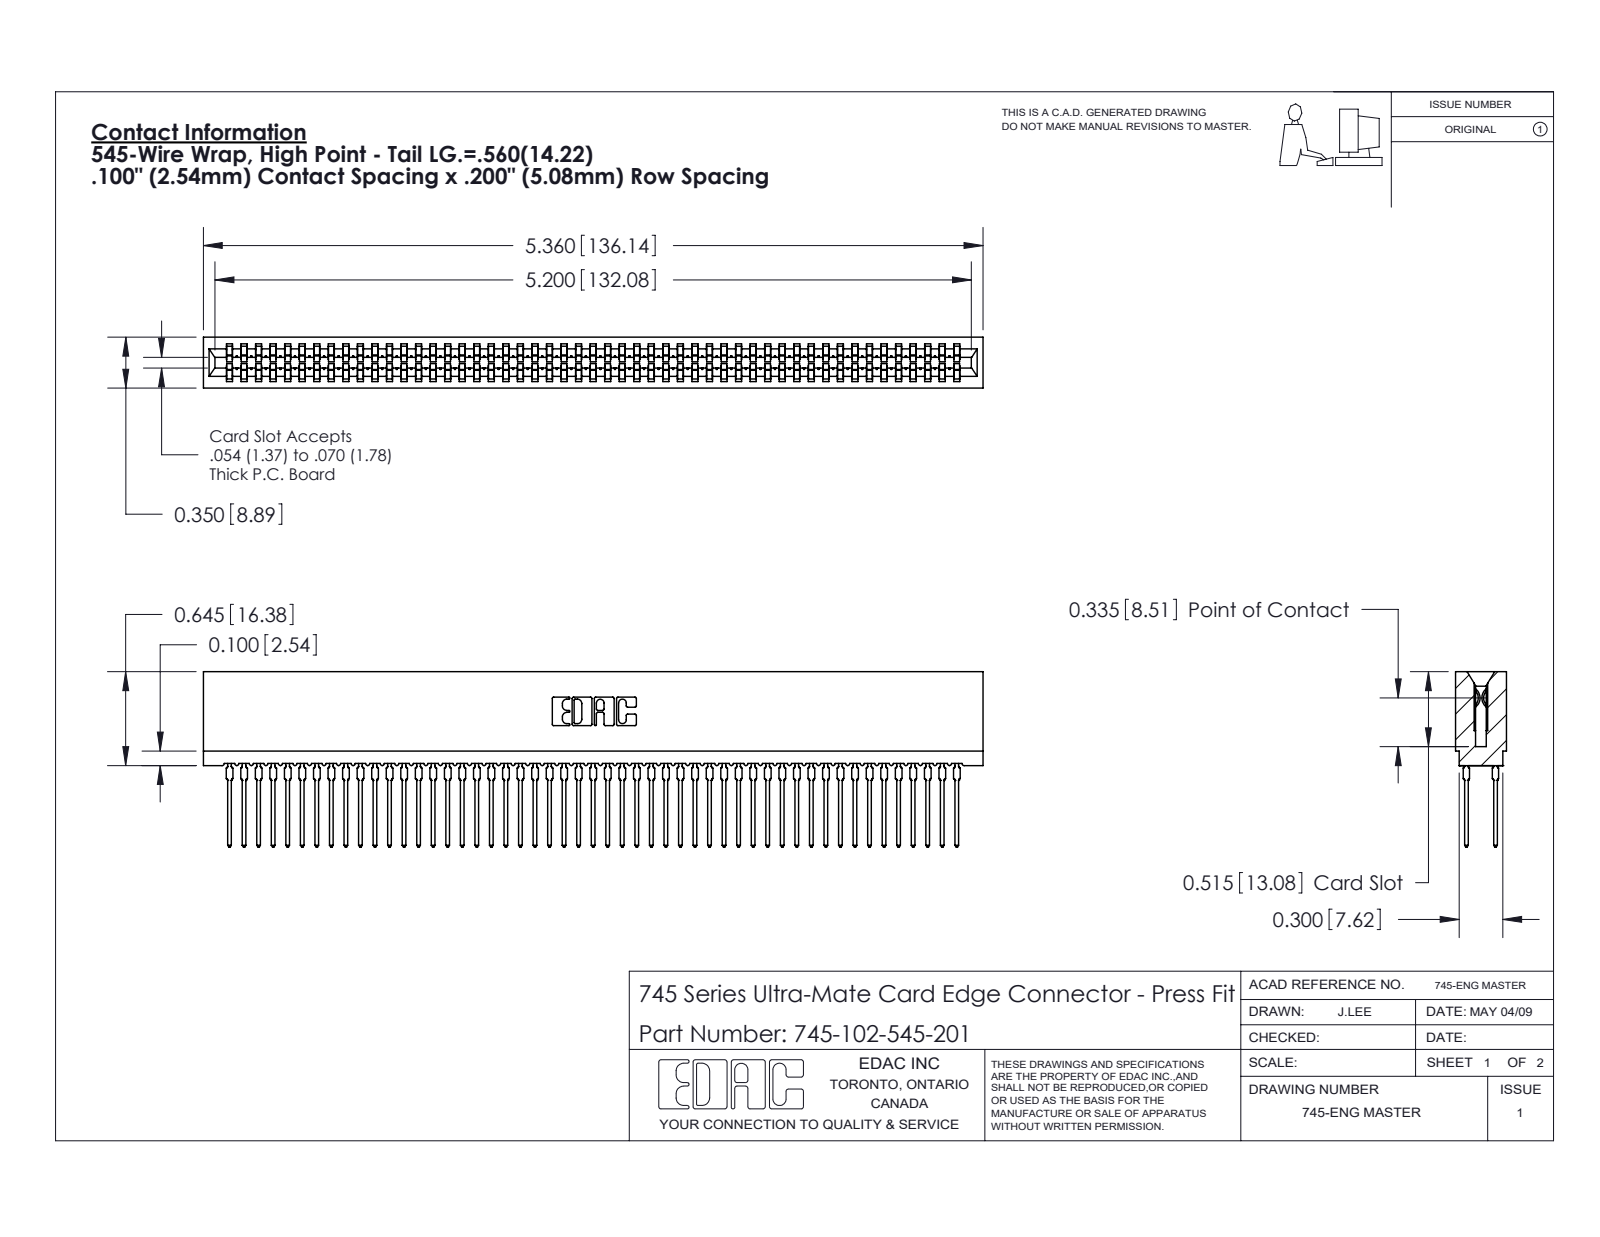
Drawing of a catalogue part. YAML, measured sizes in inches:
part_name: "745 Part_Insulator Option - 01; 745-292-001_545; 745-102-545-201"
step_written_by: "SolidWorks 2020 (CONFIG_CONTROL_DESIGN)"
units: inches
bodies: {solids: 103, faces: 9224, planar: 4747, cylindrical: 1825, other: 2652}
overall_size: [5.36, 1.206, 0.35]
volume: 0.767
surface_area: 42.33
partial_cylinders:
  - {radius: 0.021, count: 204}
  - {radius: 0.015, count: 102}
  - {radius: 0.01, count: 22}
  - {radius: 0.005, count: 8}
  - {radius: 0.011, count: 8}
  - {radius: 0.007, count: 6}
  - {radius: 0.031, count: 6}
  - {radius: 0.026, count: 3}
face_to_face_distances: [0.063, 0.287, 0.2, 0.35, 0.045, 0.305, 0.018, 0.243, 0.138, 0.212]
